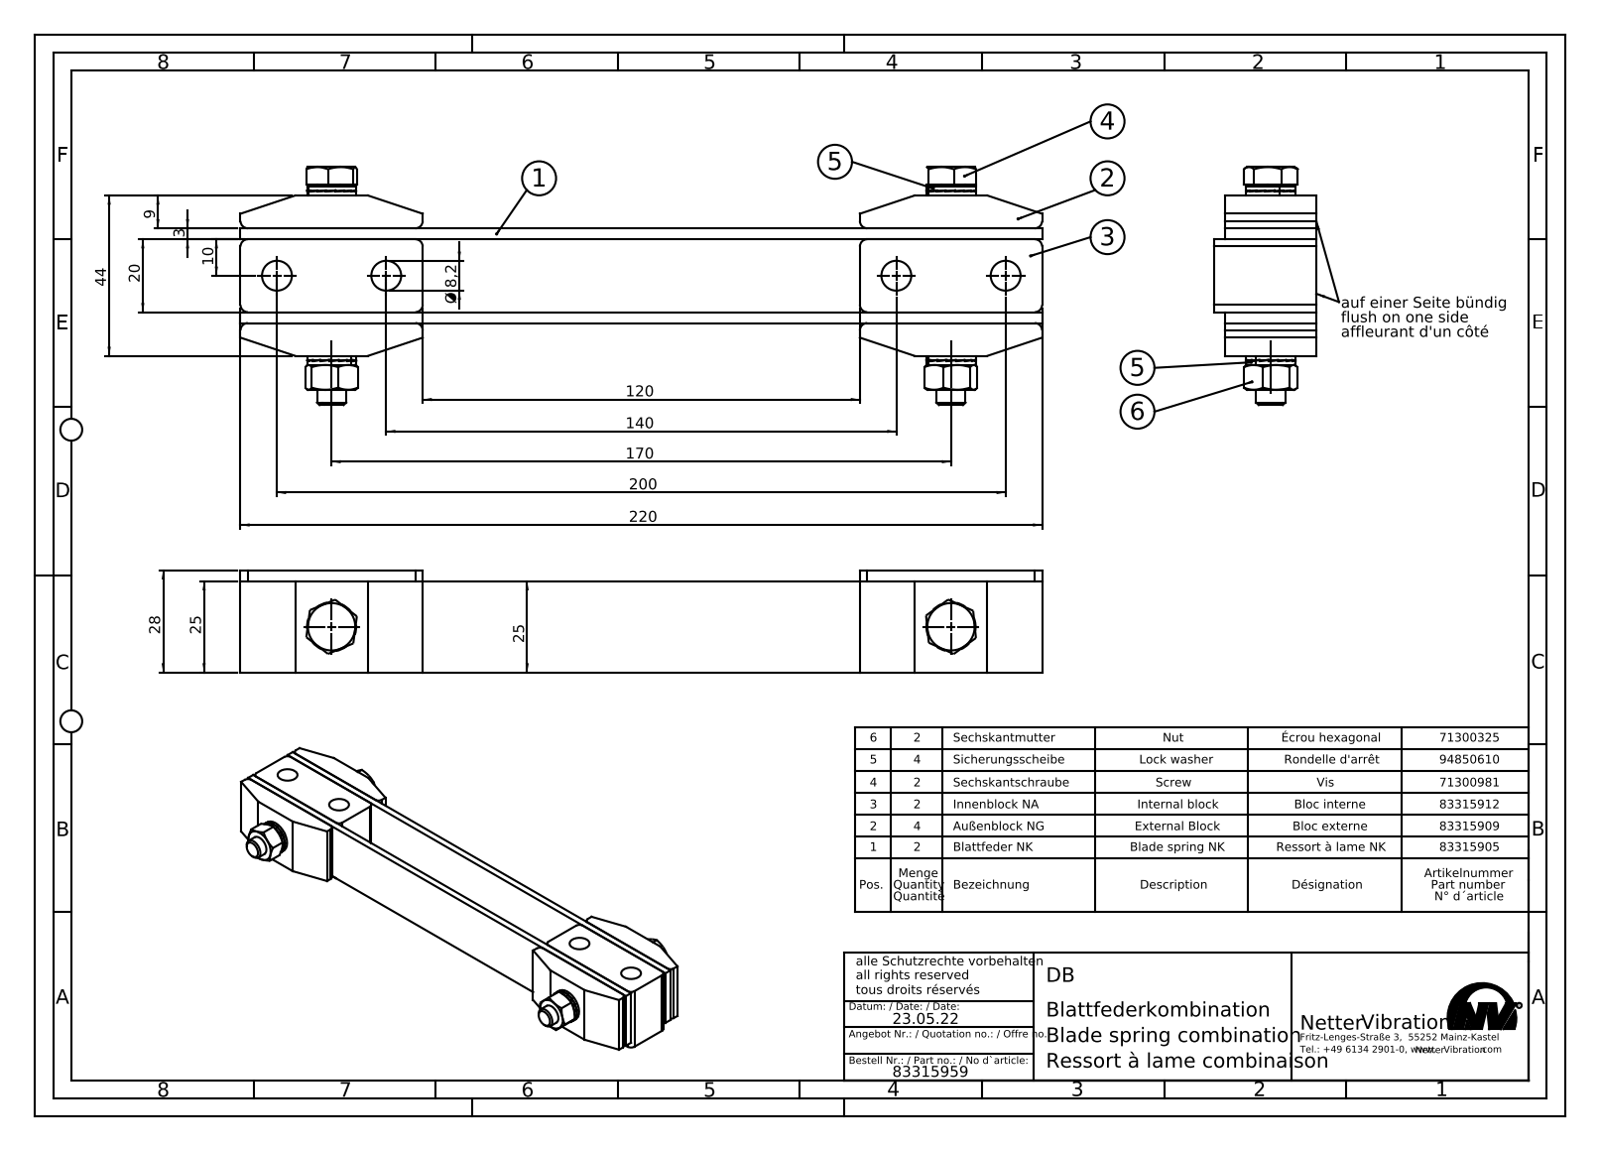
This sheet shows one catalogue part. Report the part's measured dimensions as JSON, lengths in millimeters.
{"part_name": "Blattfederkombination DB # 83315959", "step_written_by": "SolidWorks 2015 (AUTOMOTIVE_DESIGN)", "units": "millimeters", "bodies": {"solids": 16, "faces": 694, "planar": 558, "cylindrical": 84, "other": 52}, "overall_size": [220, 65.3, 28], "volume_mm3": 125385, "surface_area_mm2": 60869, "round_holes": [[8.2, 6], [6.8, 2], [8, 2], [8.5, 2], [8.7, 2]], "round_bosses_or_shafts": [[13.5, 2], [13, 2]], "partial_cylinders_radius": [[2, 16]], "face_to_face_distances": [3, 23, 20, 26, 25, 9, 12, 32, 35, 28], "hole_center_spacings": [170, 30, 140, 200]}
